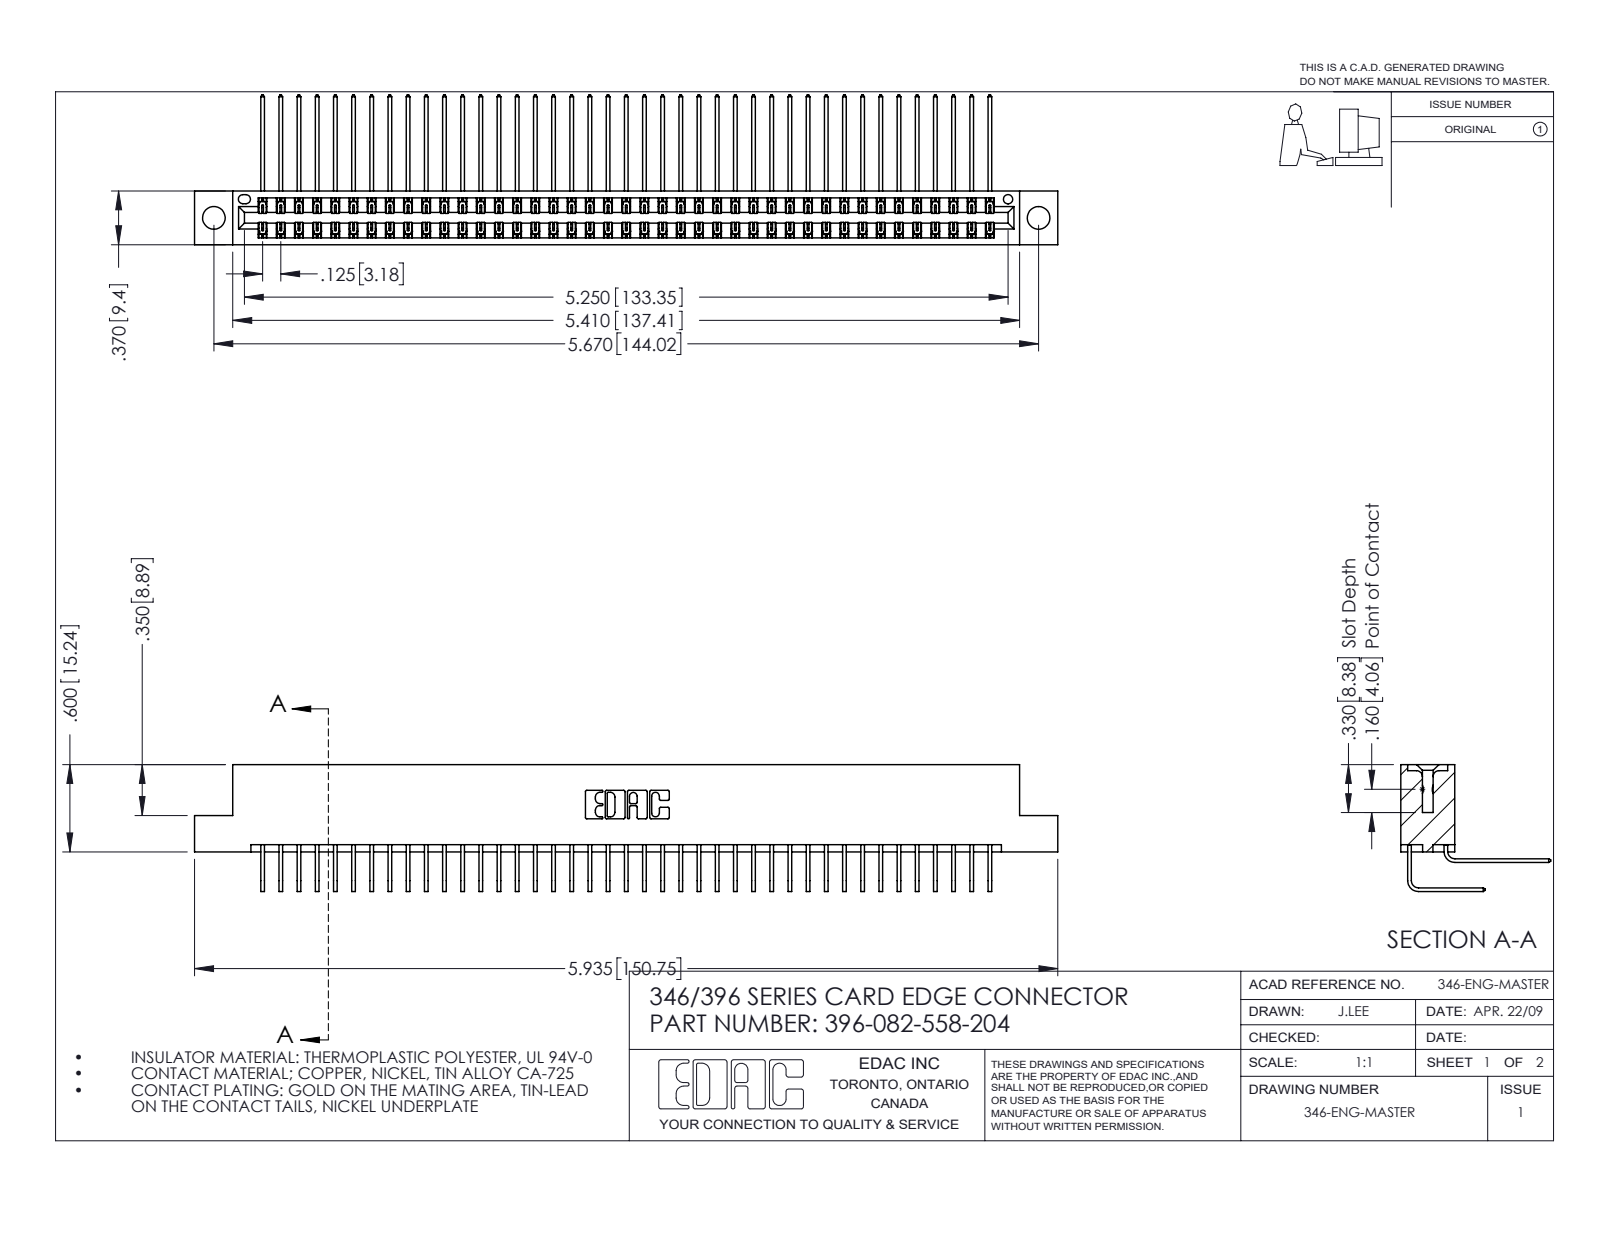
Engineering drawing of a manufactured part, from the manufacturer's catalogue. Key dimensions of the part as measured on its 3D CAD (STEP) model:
Part name (STEP PRODUCT): 345-292-001_558 559 Tail - 1; 345-292-001_558 Tail - 2; 346 Part_Flush Mounting Lugs - 0.156 Dia-TH; 396-082-558-204
STEP written by: SolidWorks 2016 (CONFIG_CONTROL_DESIGN)
Units: inches
Bodies: 83 solids, 4550 faces (3110 planar, 1440 cylindrical, 0 other)
Overall size (bounding box): 5.935 × 1.03 × 0.873
Volume: 0.92 in³ · Surface area: 35.33 in²
Round holes (diameter × count): ⌀0.156 ×2, ⌀0.064 ×1
Partial cylindrical surfaces — rounded edges, fillets, slot ends (radius × count): R0.006 ×123, R0.01 ×22, R0.007 ×6, R0.031 ×6, R0.026 ×3, R0.014 ×2, R0.022 ×2, R0.024 ×2
Main face-to-face distances: 0.322, 0.048, 0.025, 0.37, 0.298, 0.25, 0.072, 0.275, 0.148, 0.222
Hole centre spacings: 0.246, 5.461, 5.67
